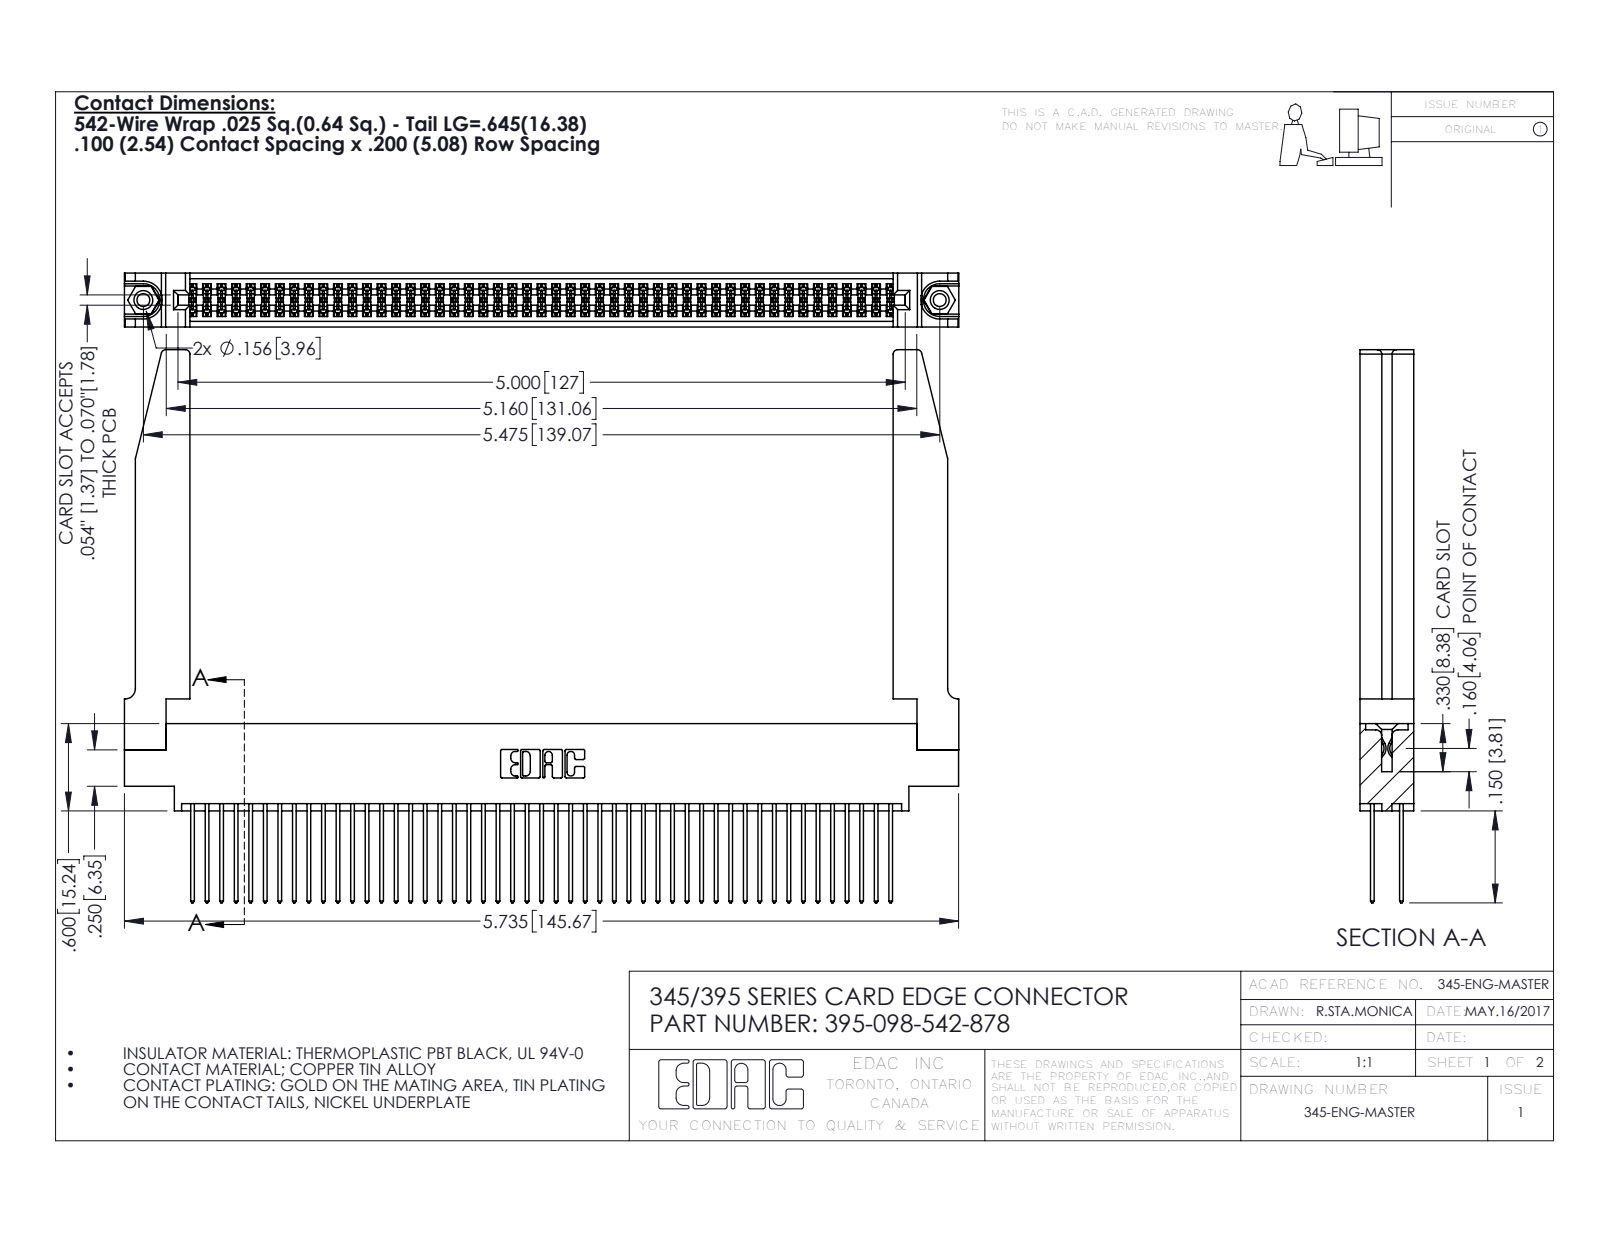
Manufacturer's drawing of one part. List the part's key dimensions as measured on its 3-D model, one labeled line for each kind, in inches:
Part name (STEP PRODUCT): 345 Part_0.170 Offset - 0.156 Dia-TH; 395-098-542-878; 345-220-078_345-220-078; 345-250-001_345-250-001-102 (+1 more)
STEP written by: SolidWorks 2016 (CONFIG_CONTROL_DESIGN)
Units: inches
Bodies: 103 solids, 5264 faces (3460 planar, 1752 cylindrical, 52 other)
Overall size (bounding box): 5.736 × 3.802 × 0.37
Volume: 1.363 in³ · Surface area: 47.7 in²
Round holes (diameter × count): ⌀0.089 ×2, ⌀0.125 ×2, ⌀0.156 ×2, ⌀0.064 ×1
Round bosses / shafts (diameter × count): ⌀0.155 ×2
Partial cylindrical surfaces — rounded edges, fillets, slot ends (radius × count): R0.006 ×147, R0.01 ×98, R0.01 ×22, R0.03 ×8, R0.007 ×6, R0.031 ×6, R0.026 ×3, R0.014 ×2
Main face-to-face distances: 0.072, 0.298, 0.37, 0.098, 0.272, 0.025, 0.2, 0.225, 0.175, 0.148
Hole centre spacings: 0.27, 5.239, 5.475
